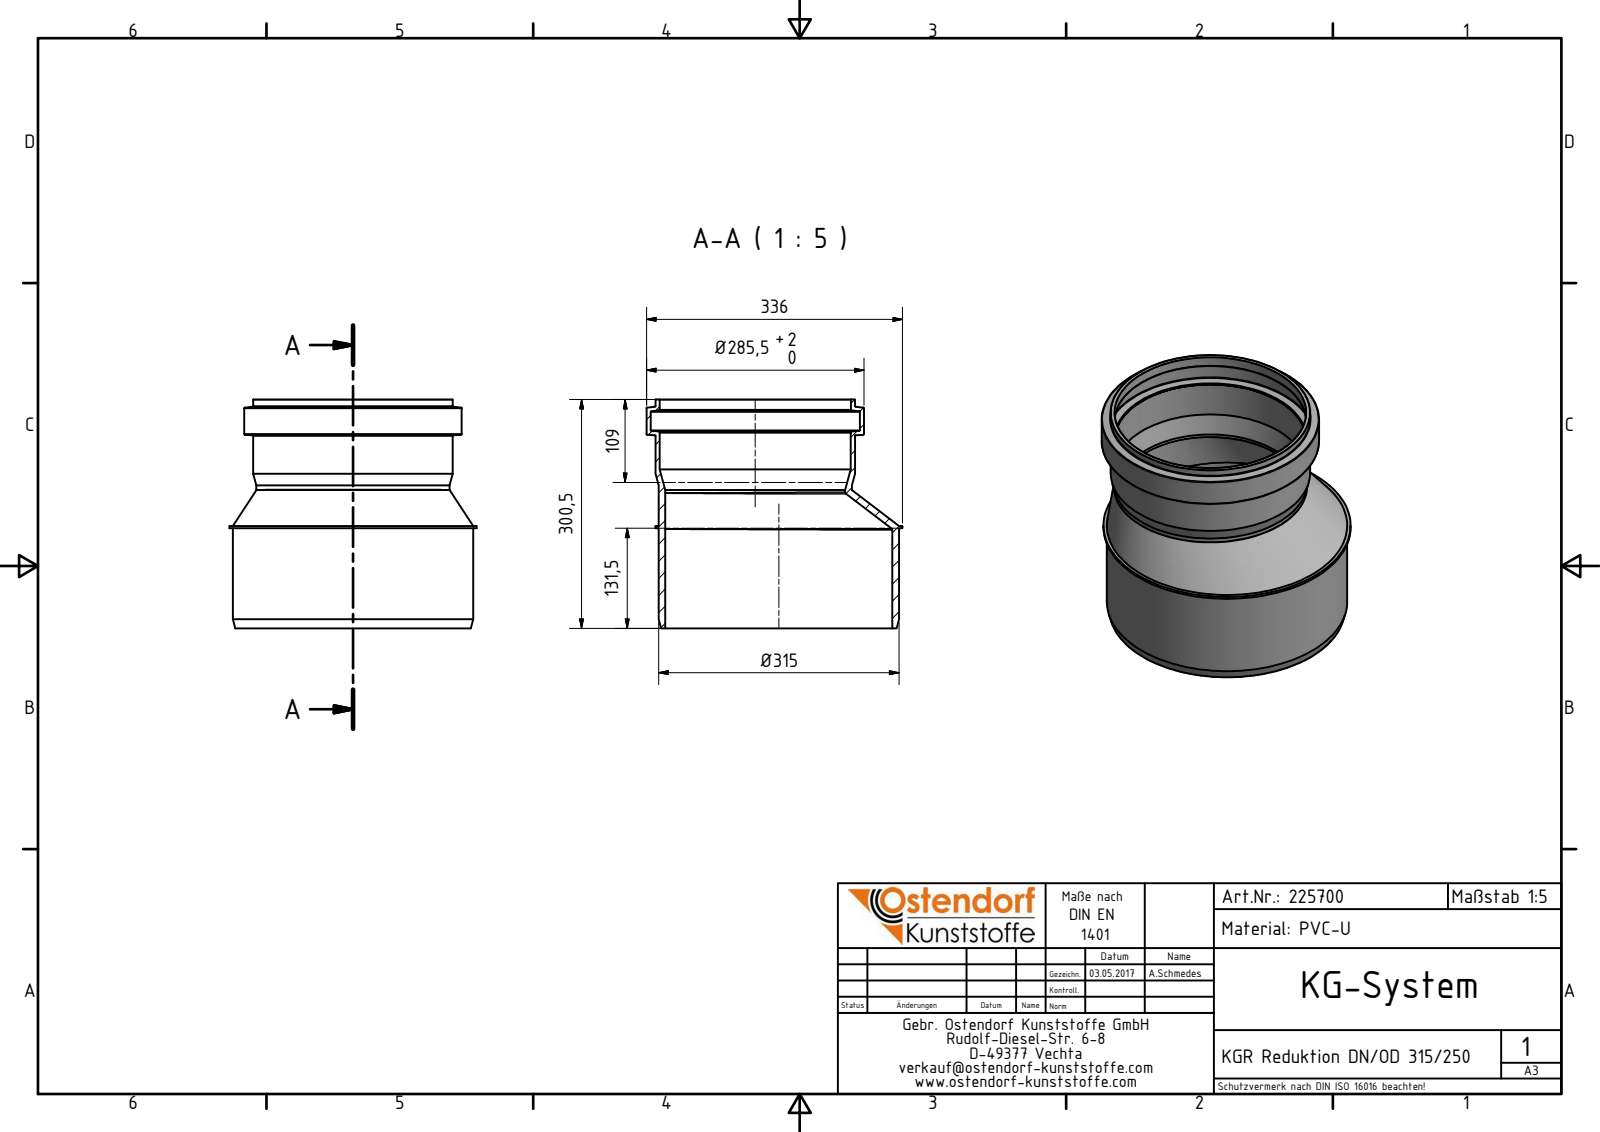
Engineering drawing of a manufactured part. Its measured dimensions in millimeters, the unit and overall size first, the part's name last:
Units: millimetres
Overall size (bounding box): 336 × 324.6 × 300.5
Round holes (diameter × count): ⌀236.3 ×1, ⌀250.8 ×1, ⌀251.1 ×1, ⌀274.5 ×1, ⌀298.2 ×1
Round bosses / shafts (diameter × count): ⌀324.6 ×1, ⌀315.6 ×1, ⌀285.5 ×1, ⌀262.1 ×1, ⌀261.8 ×1, ⌀253.7 ×1
Main face-to-face distances: 131.5, 134.5, 3, 300.5, 169, 166, 256.87, 125.37, 122.37, 43.63
Hole centre spacings: 30.95
Volume: 2 259 000 mm³ · Surface area: 609 981 mm²
Bodies: 1 solid, 39 faces (5 planar, 12 cylindrical, 22 other)
Part name (STEP PRODUCT): 225700 KGR Reduktion DN_OD 315_250
STEP written by: Autodesk Inventor 2016 (AUTOMOTIVE_DESIGN)
